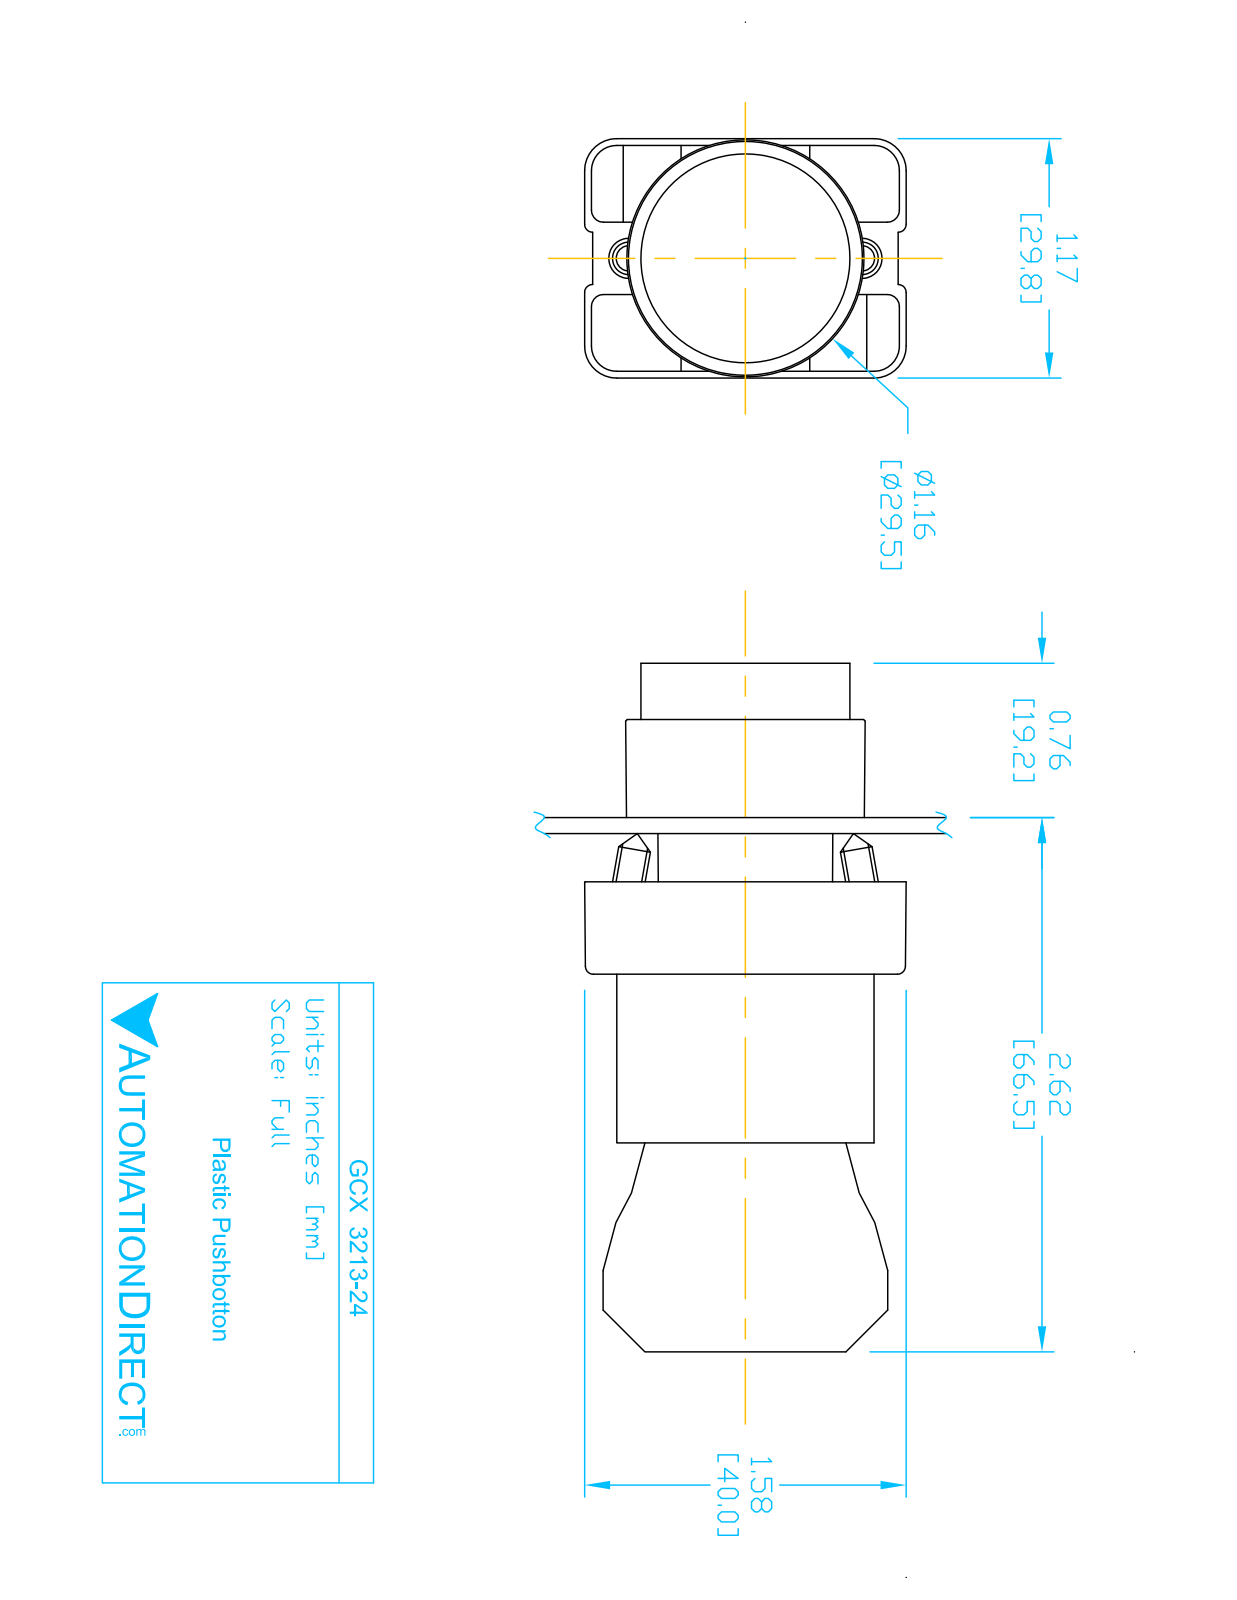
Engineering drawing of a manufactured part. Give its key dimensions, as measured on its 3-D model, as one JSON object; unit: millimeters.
{"part_name": "ECX3029-2; GCX3213-24; ecx1040; GCX3213 OPERATOR (+1 more)", "step_written_by": "SolidWorks 2016 (AUTOMOTIVE_DESIGN)", "units": "millimeters", "bodies": {"solids": 7, "faces": 425, "planar": 250, "cylindrical": 144, "other": 31}, "overall_size": [84.3, 40.2, 29.9], "volume_mm3": 44590, "surface_area_mm2": 23430, "round_holes": [[2, 2], [3.1, 2], [3.3, 2], [2.2, 1], [5, 1], [11.9, 1], [22.3, 1], [22.6, 1], [26, 1]], "round_bosses_or_shafts": [[4, 4], [29.8, 1], [25.5, 1], [24, 1], [21.7, 1], [19.8, 1], [12.8, 1]], "partial_cylinders_radius": [[1.5, 24], [1, 12], [3.1, 12], [4, 12], [1, 8], [3.3, 2], [0.5, 1], [1.6, 1]], "face_to_face_distances": [21, 14.7, 29.7, 51.3, 30.3, 0.8, 0.8, 14.6, 29.6, 15.1], "hole_center_spacings": [6, 13.8, 12, 12.4]}
